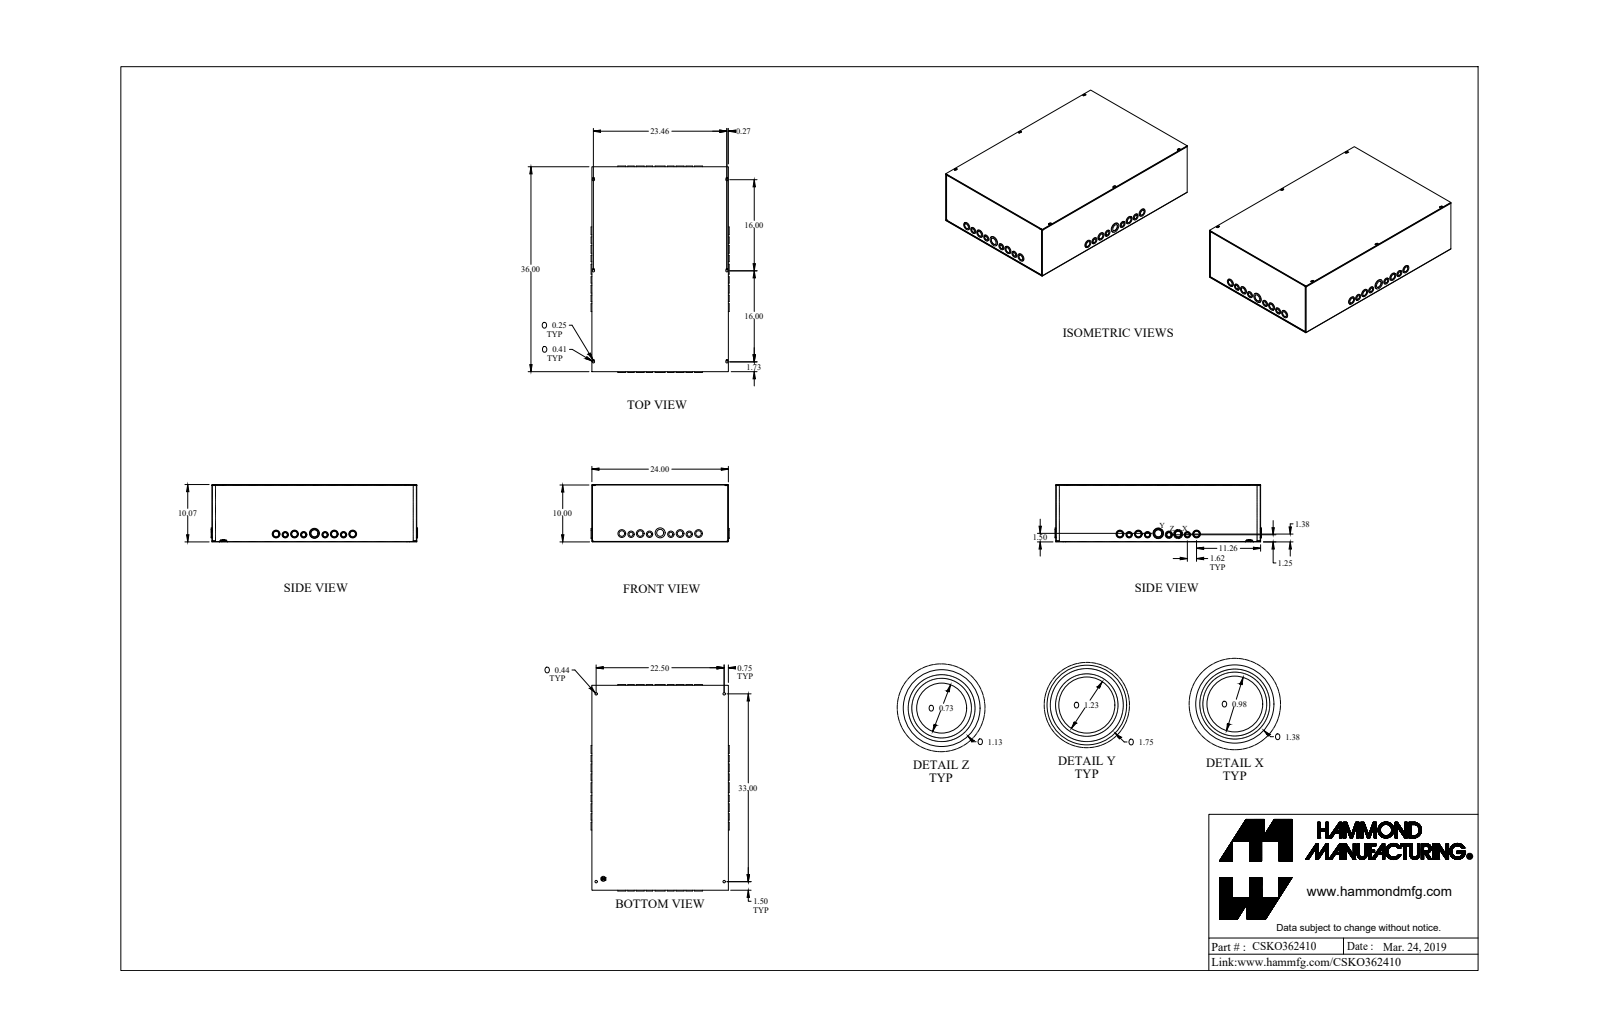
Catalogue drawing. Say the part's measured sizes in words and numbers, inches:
The part is named "CSKO362410_Default". Its 3-D file was written by "SolidWorks 2019 (CONFIG_CONTROL_DESIGN)". It is 4 solids with 653 faces: 273 planar, 372 cylindrical and 8 other. Overall it measures 36.264 by 24.264 by 10.072 inches. Its volume is 218.1 cubic inches and its surface area 6 090 square inches. Round holes: 16 of diameter 0.981, 10 of diameter 1.231, 8 of diameter 0.731, 7 of diameter 0.17, 4 of diameter 0.437, 2 of diameter 1.606, 1 of diameter 0.5. Round bosses or shafts: 14 of diameter 1.125, 9 of diameter 1.375, 8 of diameter 0.875, 6 of diameter 0.875, 4 of diameter 1.125, 2 of diameter 1.75, 1 of diameter 1.375, 1 of diameter 0.492. Partial cylindrical surfaces (rounded edges, fillets, slot ends): 12 of radius 0.036, 12 of radius 0.108, 8 of radius 0.072, 6 of radius 0.125, 6 of radius 0.203. The main face-to-face distances are 0.072, 10, 9.928, 10.072, 23.928, 35.928, 24, 23.856, 36, 35.856. The hole center spacings are 1.625, 3.24, 8.621, 7, 10.24, 0.693, 1.896, 3.502.
